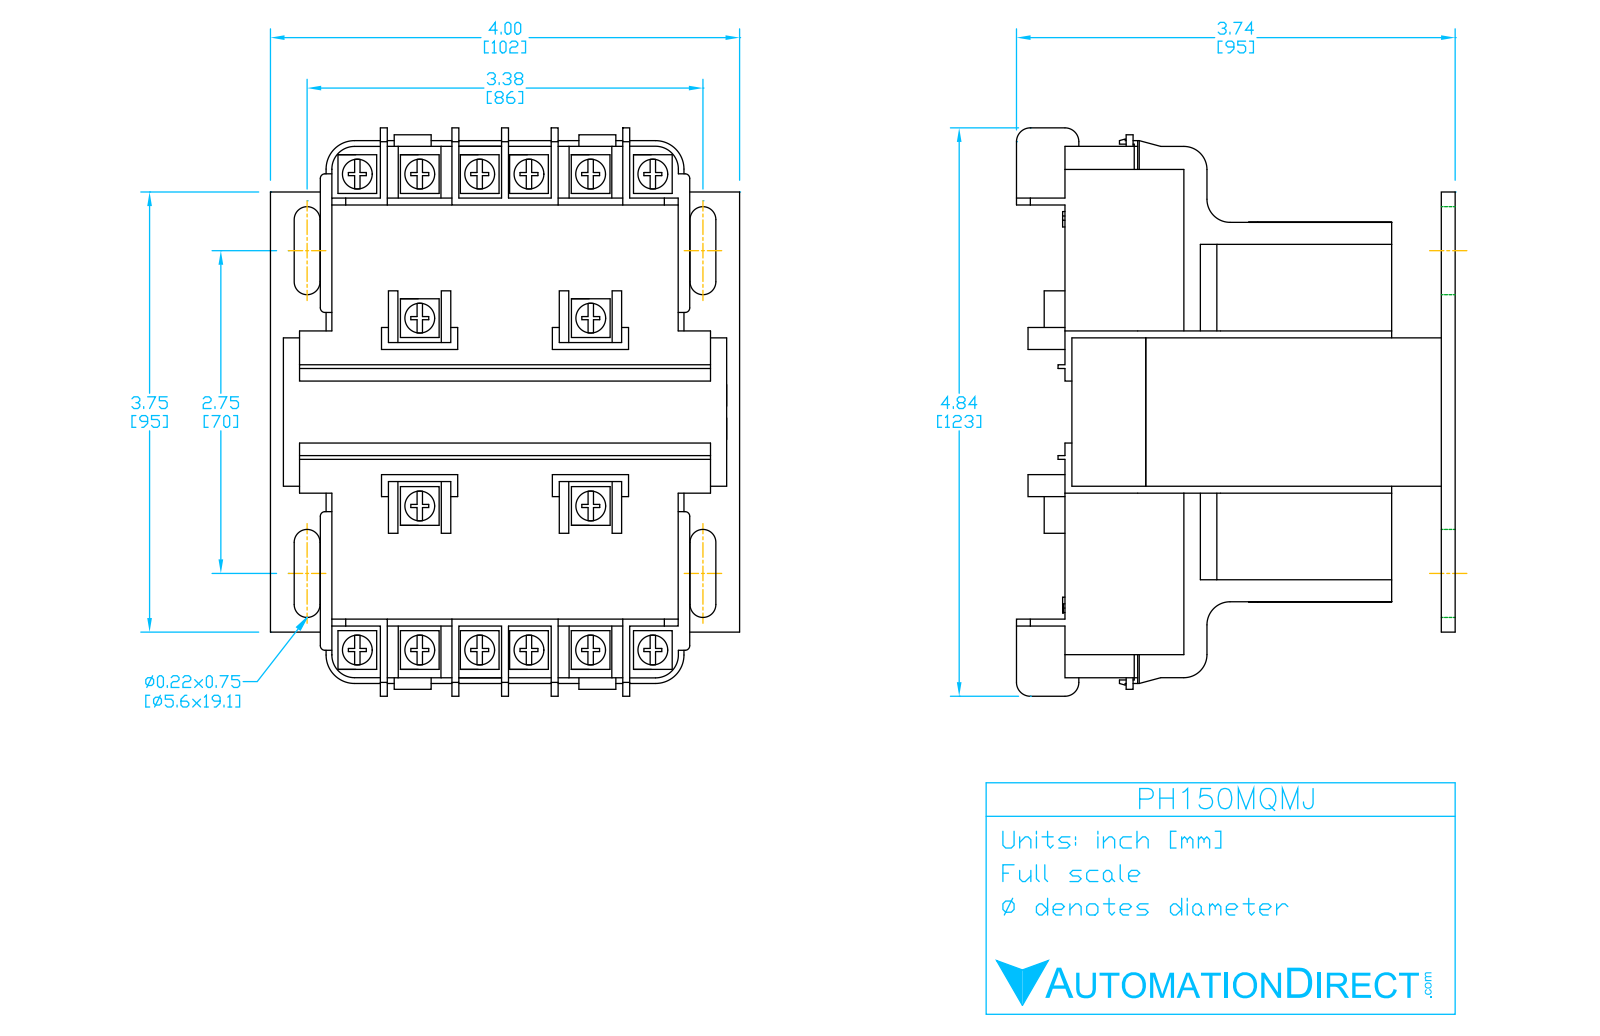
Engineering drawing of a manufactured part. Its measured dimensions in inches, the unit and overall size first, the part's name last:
Units: inches
Overall size (bounding box): 4.839 × 4 × 3.74
Round holes (diameter × count): ⌀0.157 ×4
Partial cylindrical surfaces — rounded edges, fillets, slot ends (radius × count): R0.039 ×62, R0.099 ×21, R0.197 ×16, R0.11 ×8, R0.137 ×5, R0.1 ×4, R0.188 ×4, R0.243 ×4
Main face-to-face distances: 1.26, 0.06, 1.033, 0.118, 0.069, 1.102, 0.413, 2.52, 2.589, 3.622
Hole centre spacings: 0.787, 3.375, 3.465
Volume: 35.22 in³ · Surface area: 182 in²
Bodies: 8 solids, 657 faces (386 planar, 194 cylindrical, 77 other)
Part name (STEP PRODUCT): PH150MQMJ
STEP written by: SolidWorks 2017 (AUTOMOTIVE_DESIGN)
